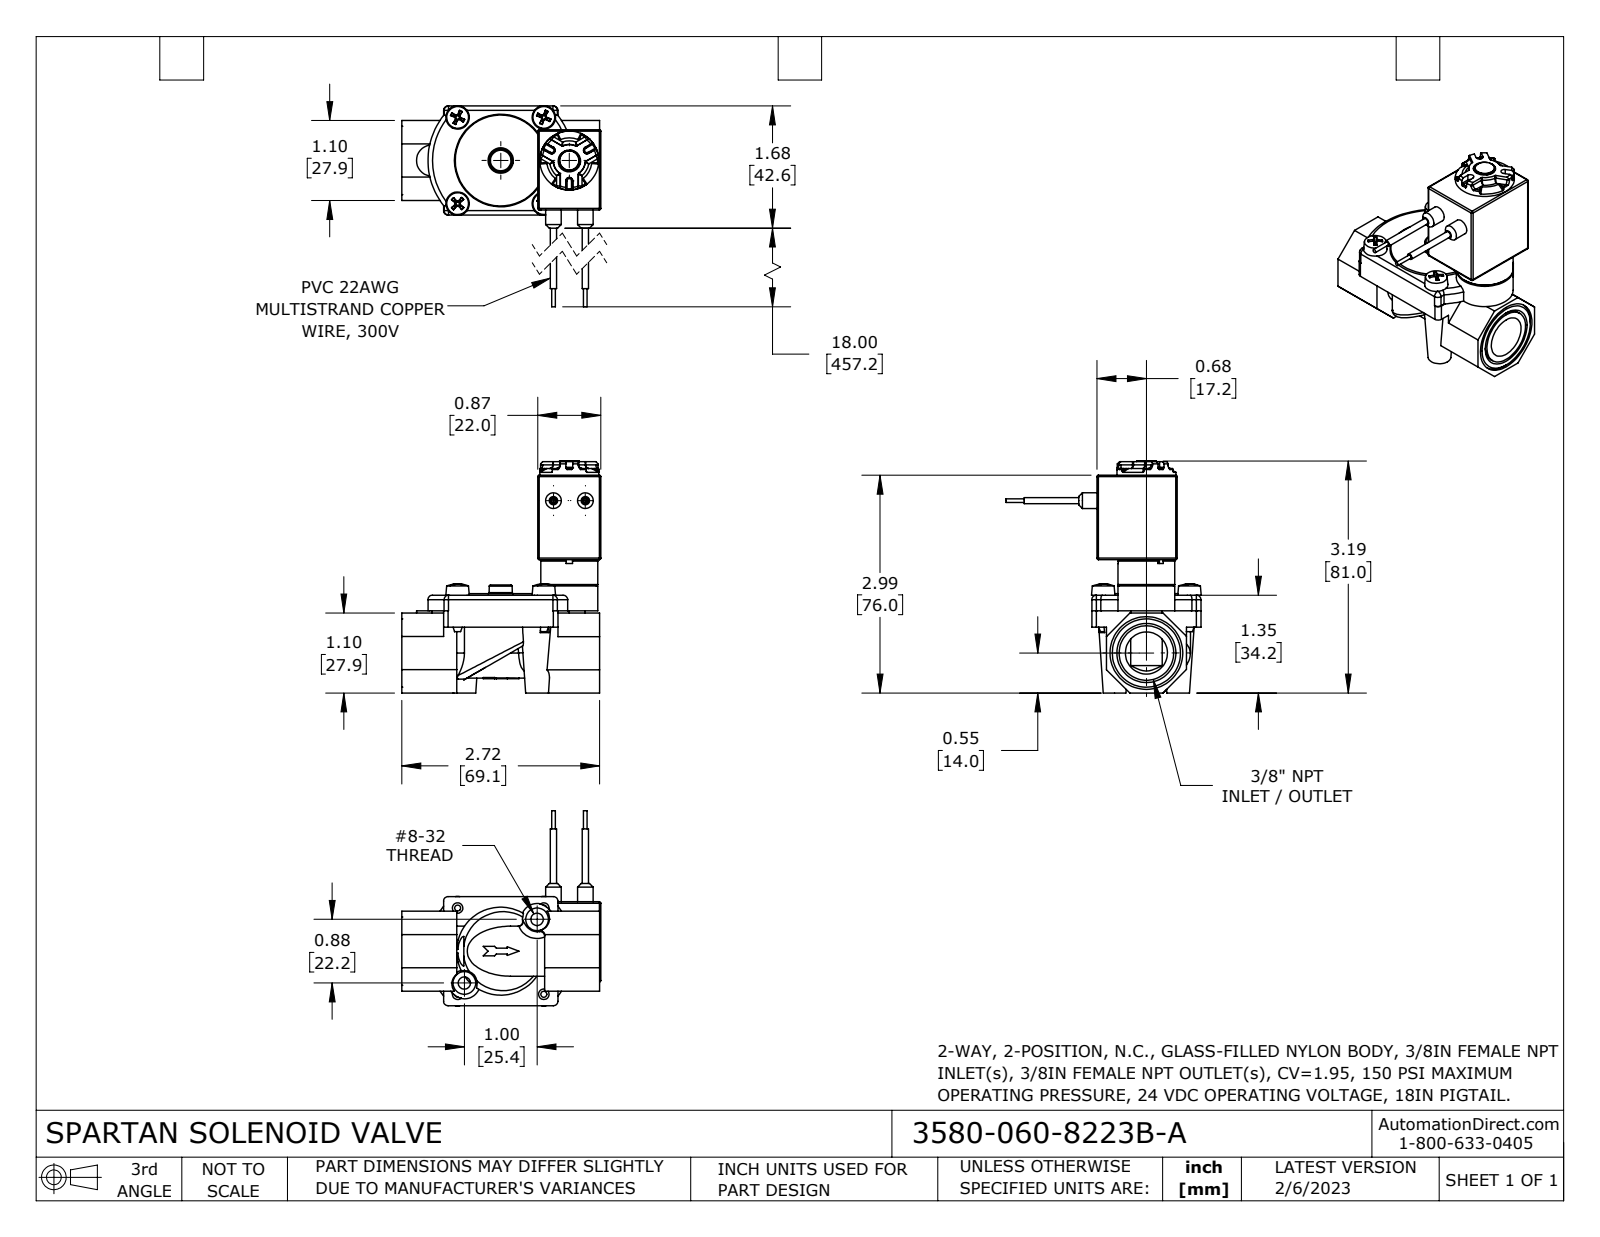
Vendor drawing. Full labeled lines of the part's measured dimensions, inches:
Part name (STEP PRODUCT): 3580-060-8223B-A
STEP written by: SolidWorks 2021 (CONFIG_CONTROL_DESIGN)
Units: inches
Bodies: 1 solid, 631 faces (206 planar, 166 cylindrical, 259 other)
Overall size (bounding box): 3.189 × 2.736 × 2.683
Volume: 3.58 in³ · Surface area: 43.23 in²
Round holes (diameter × count): ⌀0.144 ×4, ⌀0.093 ×2, ⌀0.17 ×2, ⌀0.36 ×2, ⌀0.062 ×1, ⌀0.156 ×1, ⌀0.268 ×1, ⌀0.285 ×1, ⌀0.312 ×1, ⌀0.315 ×1, ⌀0.321 ×1, ⌀0.472 ×1
Round bosses / shafts (diameter × count): ⌀0.125 ×4, ⌀0.215 ×2, ⌀0.085 ×2, ⌀0.05 ×2, ⌀1.375 ×1, ⌀0.782 ×1, ⌀0.781 ×1, ⌀0.75 ×1
Partial cylindrical surfaces — rounded edges, fillets, slot ends (radius × count): R0.02 ×12, R0.062 ×12, R0.015 ×6, R0.05 ×6, R0.044 ×3, R0.215 ×2, R0.304 ×1, R0.344 ×1
Main face-to-face distances: 1.1, 0.866, 0.2, 1.3, 0.02, 1.102, 1.365, 0.129, 0.127, 0.973
Hole centre spacings: 0.838, 1.185, 0.181, 0.664, 0.688, 0.943, 1.034, 1.104
